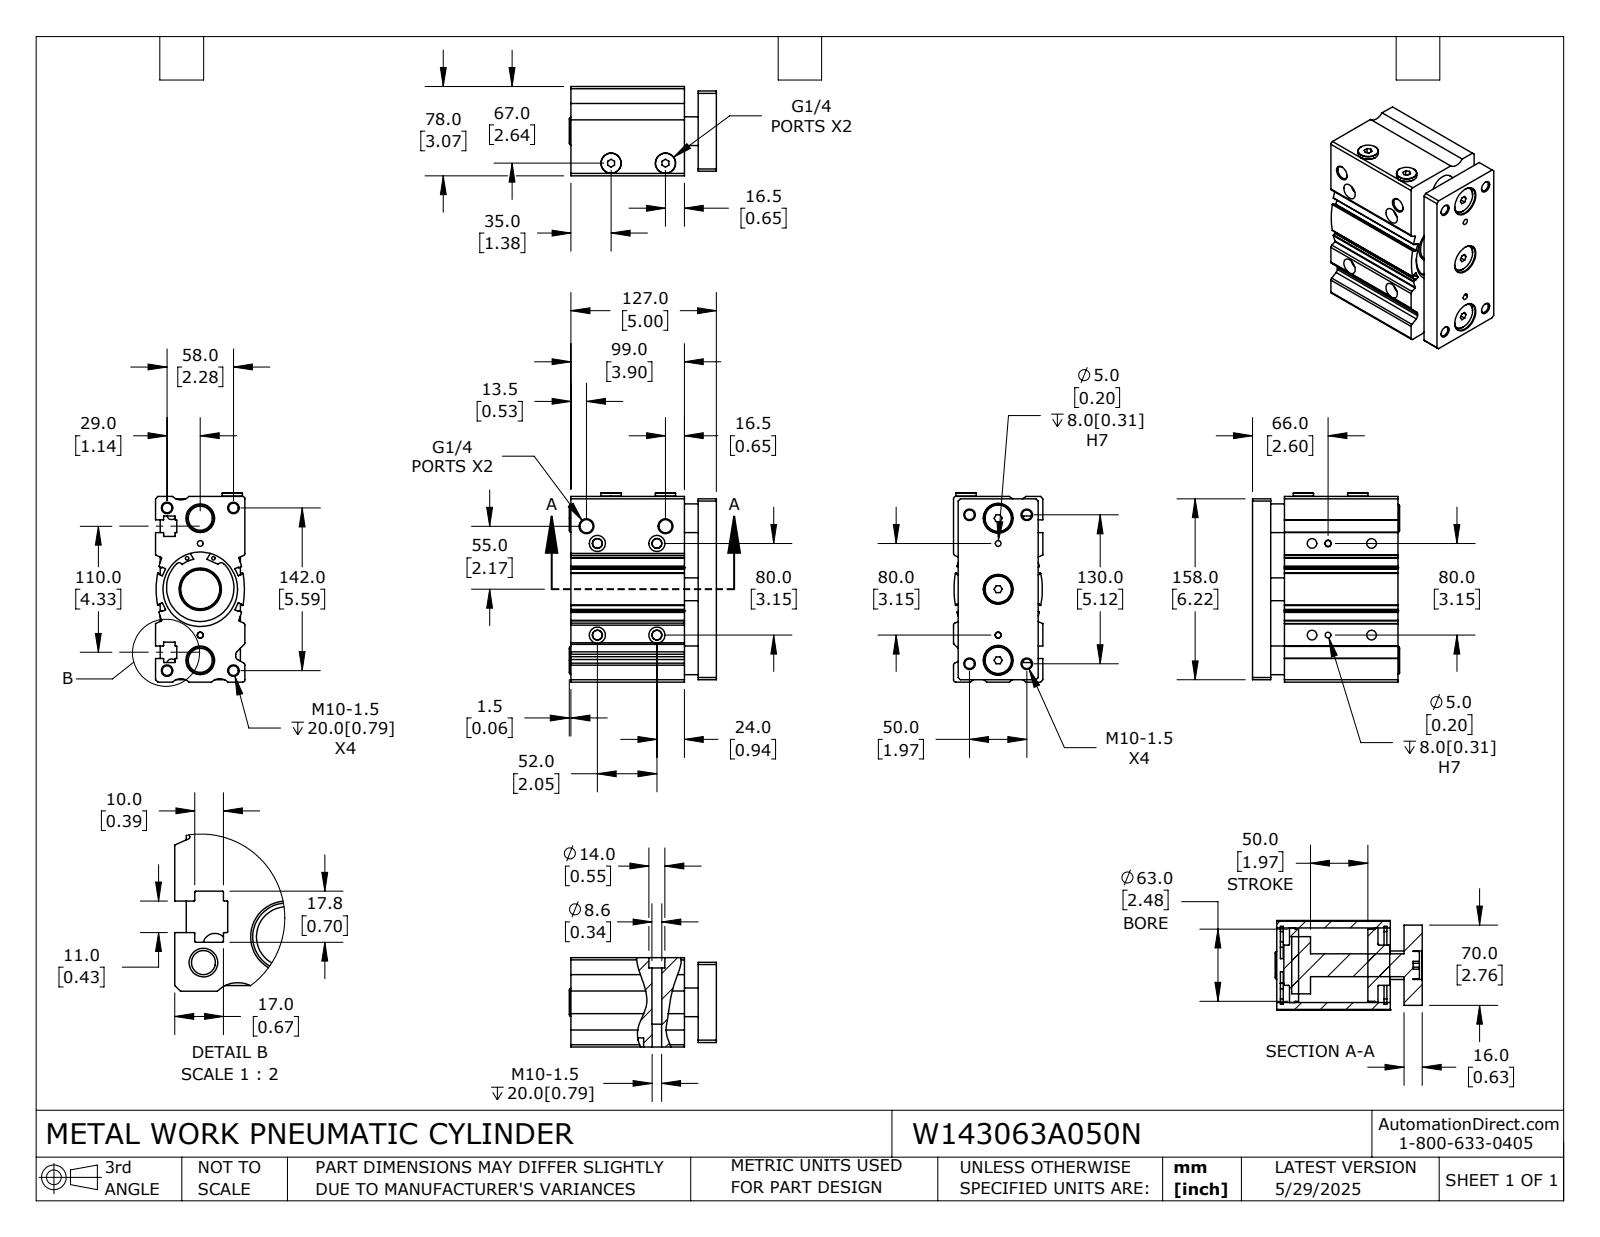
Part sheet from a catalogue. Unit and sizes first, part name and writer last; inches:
Units: inches
Overall size (bounding box): 6.496 × 5.059 × 3.071
Round holes (diameter × count): ⌀0.33 ×12, ⌀0.118 ×4, ⌀0.197 ×4, ⌀0.339 ×4, ⌀0.551 ×4, ⌀0.984 ×3, ⌀0.448 ×2, ⌀2.559 ×1
Round bosses / shafts (diameter × count): ⌀0.945 ×3, ⌀0.697 ×2, ⌀2.677 ×1, ⌀2.551 ×1, ⌀2.48 ×1, ⌀1.969 ×1, ⌀1.378 ×1, ⌀0.787 ×1
Partial cylindrical surfaces — rounded edges, fillets, slot ends (radius × count): R0.012 ×44, R0.02 ×12, R0.079 ×8, R0.098 ×4, R0.118 ×4, R0.394 ×3, R0.124 ×2, R1.157 ×2
Main face-to-face distances: 0.63, 3.898, 0.472, 1.102, 3.071, 5, 4.37, 0.157, 2.913, 6.378
Hole centre spacings: 0.284, 0.682, 0.991, 1.158, 1.195, 1.392, 1.448, 1.585
Volume: 66.8 in³ · Surface area: 331.7 in²
Bodies: 6 solids, 454 faces (182 planar, 216 cylindrical, 56 other)
Part name (STEP PRODUCT): W143063A050N; W143063A050N_ROD; W143063A050N_BODY
STEP written by: SolidWorks 2024 (CONFIG_CONTROL_DESIGN)
